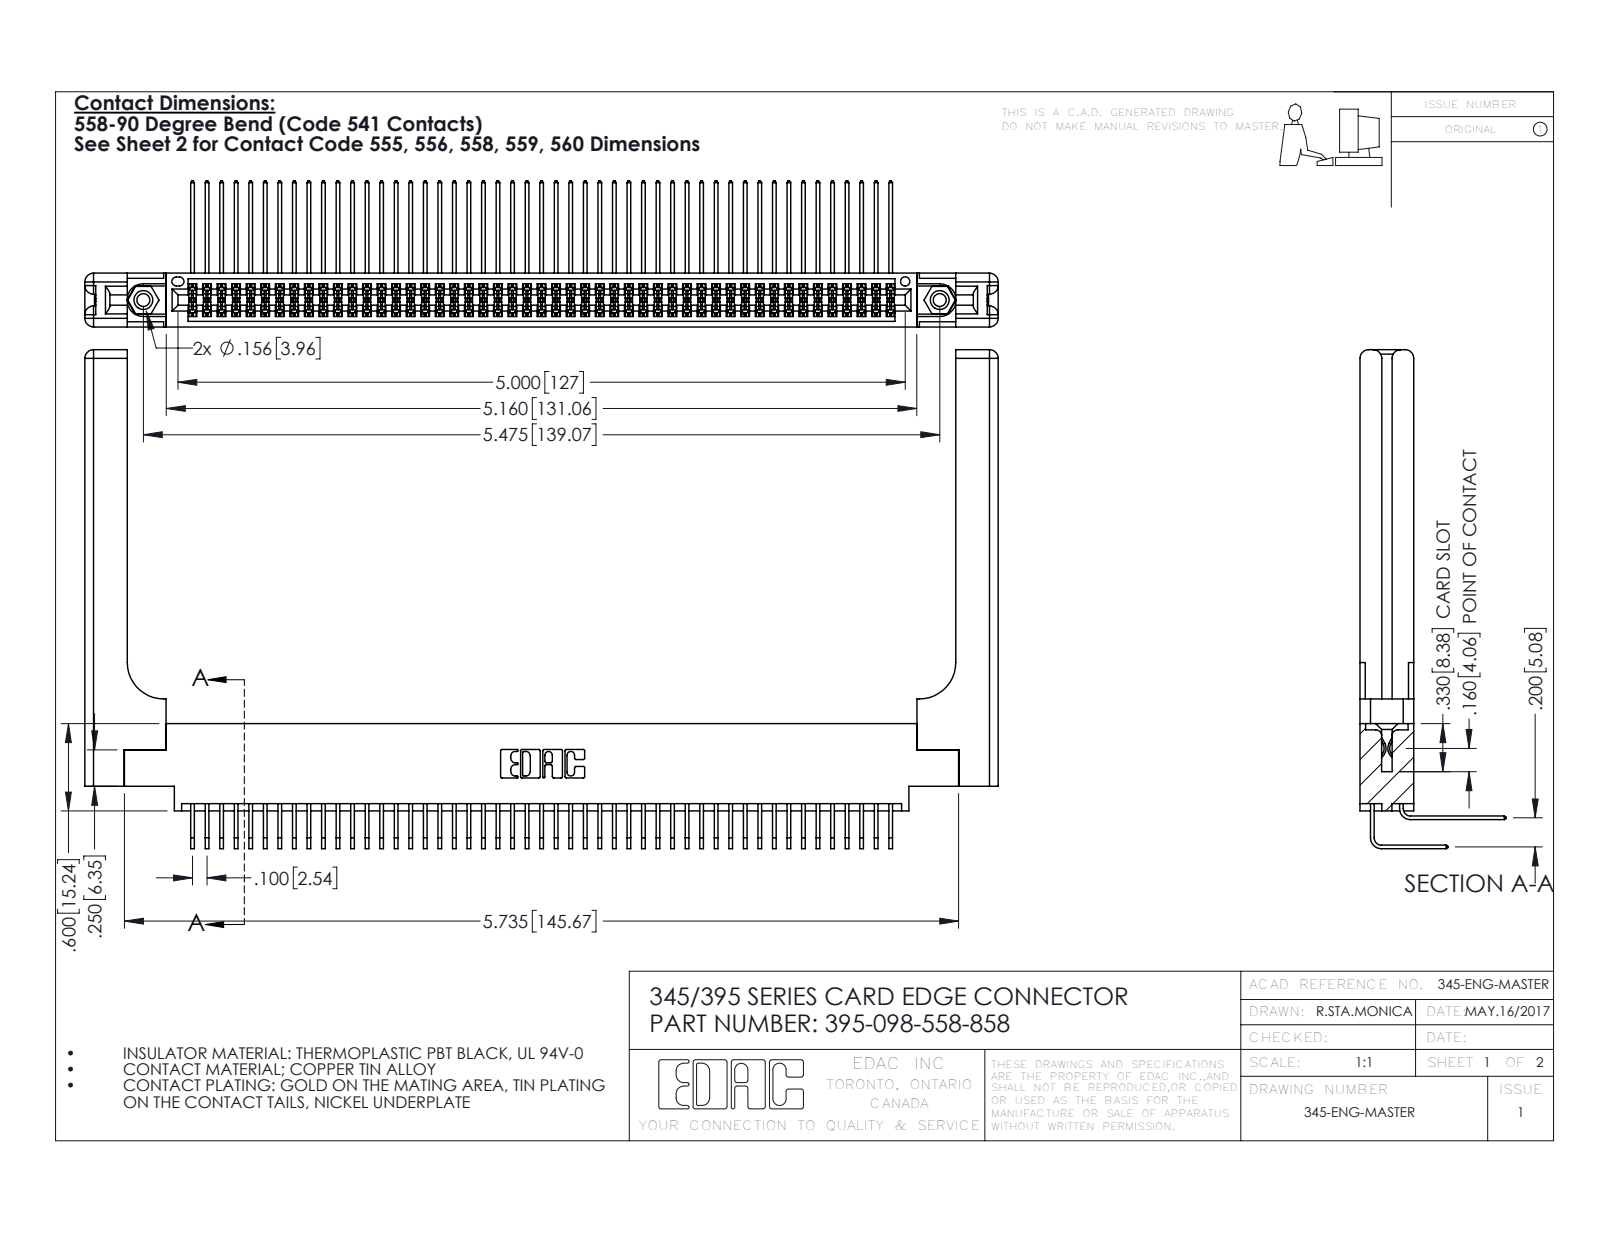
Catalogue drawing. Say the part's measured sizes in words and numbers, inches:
The part is named "345 Part_0.170 Offset - 0.156 Dia-TH; 345-292-001_558 559 Tail - 1; 395-098-558-858; 345-250-001_345-250-001-102 (+2 more)". Its 3-D file was written by "SolidWorks 2016 (CONFIG_CONTROL_DESIGN)". It is 103 solids with 5482 faces: 3662 planar, 1760 cylindrical and 60 other. Overall it measures 6.279 by 3.429 by 1.005 inches. Its volume is 1.494 cubic inches and its surface area 49.07 square inches. Round holes: 2 of diameter 0.089, 2 of diameter 0.125, 2 of diameter 0.156, 1 of diameter 0.064. Round bosses or shafts: 2 of diameter 0.155. Partial cylindrical surfaces (rounded edges, fillets, slot ends): 148 of radius 0.006, 22 of radius 0.01, 16 of radius 0.06, 6 of radius 0.007, 6 of radius 0.031, 3 of radius 0.026, 2 of radius 0.014, 2 of radius 0.019. The main face-to-face distances are 0.072, 0.37, 0.298, 0.2, 0.098, 0.272, 0.025, 0.225, 0.175, 0.148. The hole center spacings are 0.27, 5.239, 5.475.
